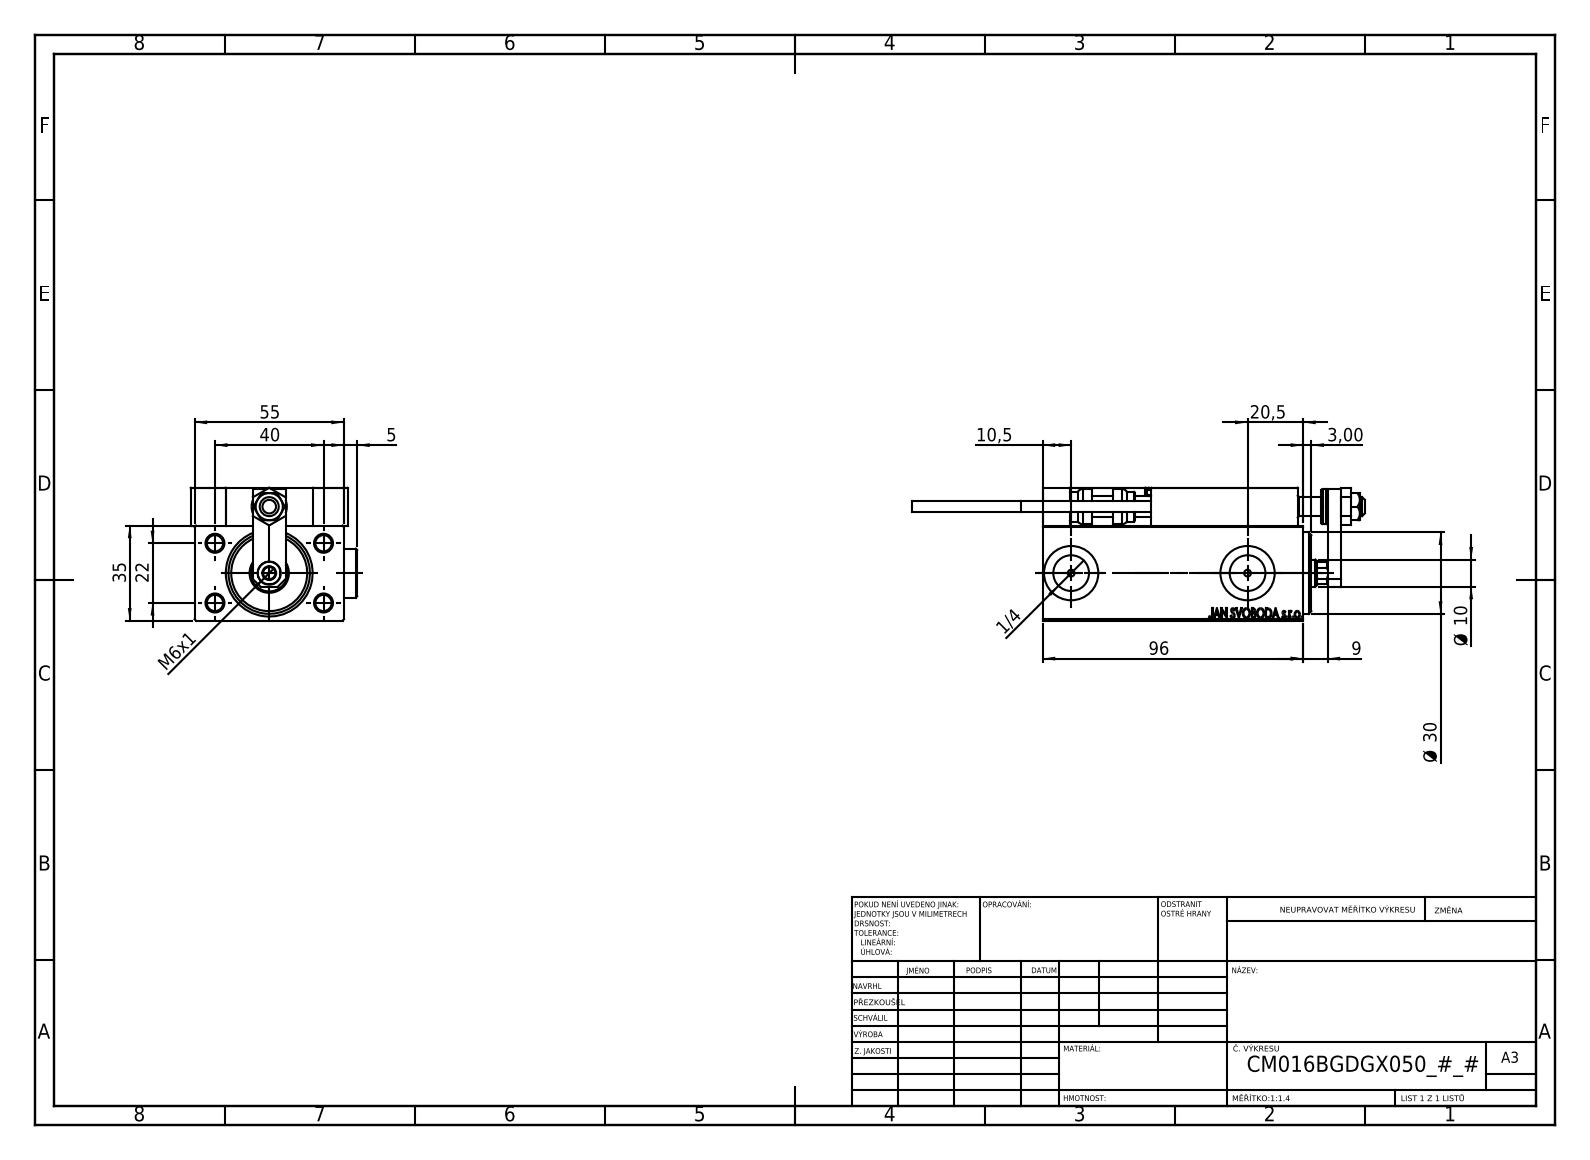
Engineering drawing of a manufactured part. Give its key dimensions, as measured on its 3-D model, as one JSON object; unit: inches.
{"part_name": "TYC_L79; NUT_D10; KONCOVKA; V450CM_B_VCP (+7 more)", "step_written_by": "SolidWorks 2019 (CONFIG_CONTROL_DESIGN)", "units": "inches", "bodies": {"solids": 26, "faces": 1372, "planar": 595, "cylindrical": 200, "other": 577}, "overall_size": [6.563, 2.417, 1.929], "volume_in3": 13.23, "surface_area_in2": 94.37, "round_holes": [[0.315, 5], [0.126, 4], [0.157, 4], [0.236, 4], [0.098, 2], [0.197, 2], [0.518, 2], [0.787, 2], [0.177, 1], [0.276, 1], [0.335, 1], [0.394, 1]], "round_bosses_or_shafts": [[0.709, 2], [0.197, 2], [0.15, 2], [0.512, 1], [0.433, 1]], "partial_cylinders_radius": [[0.012, 30], [0.118, 2], [0.177, 1]], "face_to_face_distances": [1.378, 0.551, 0.197, 2.165, 1.929, 0.118, 0.059, 0.394, 0.276, 0.512], "hole_center_spacings": [0.899, 0.448, 0.787, 0.866, 0.95, 1.165, 1.169, 1.42]}
